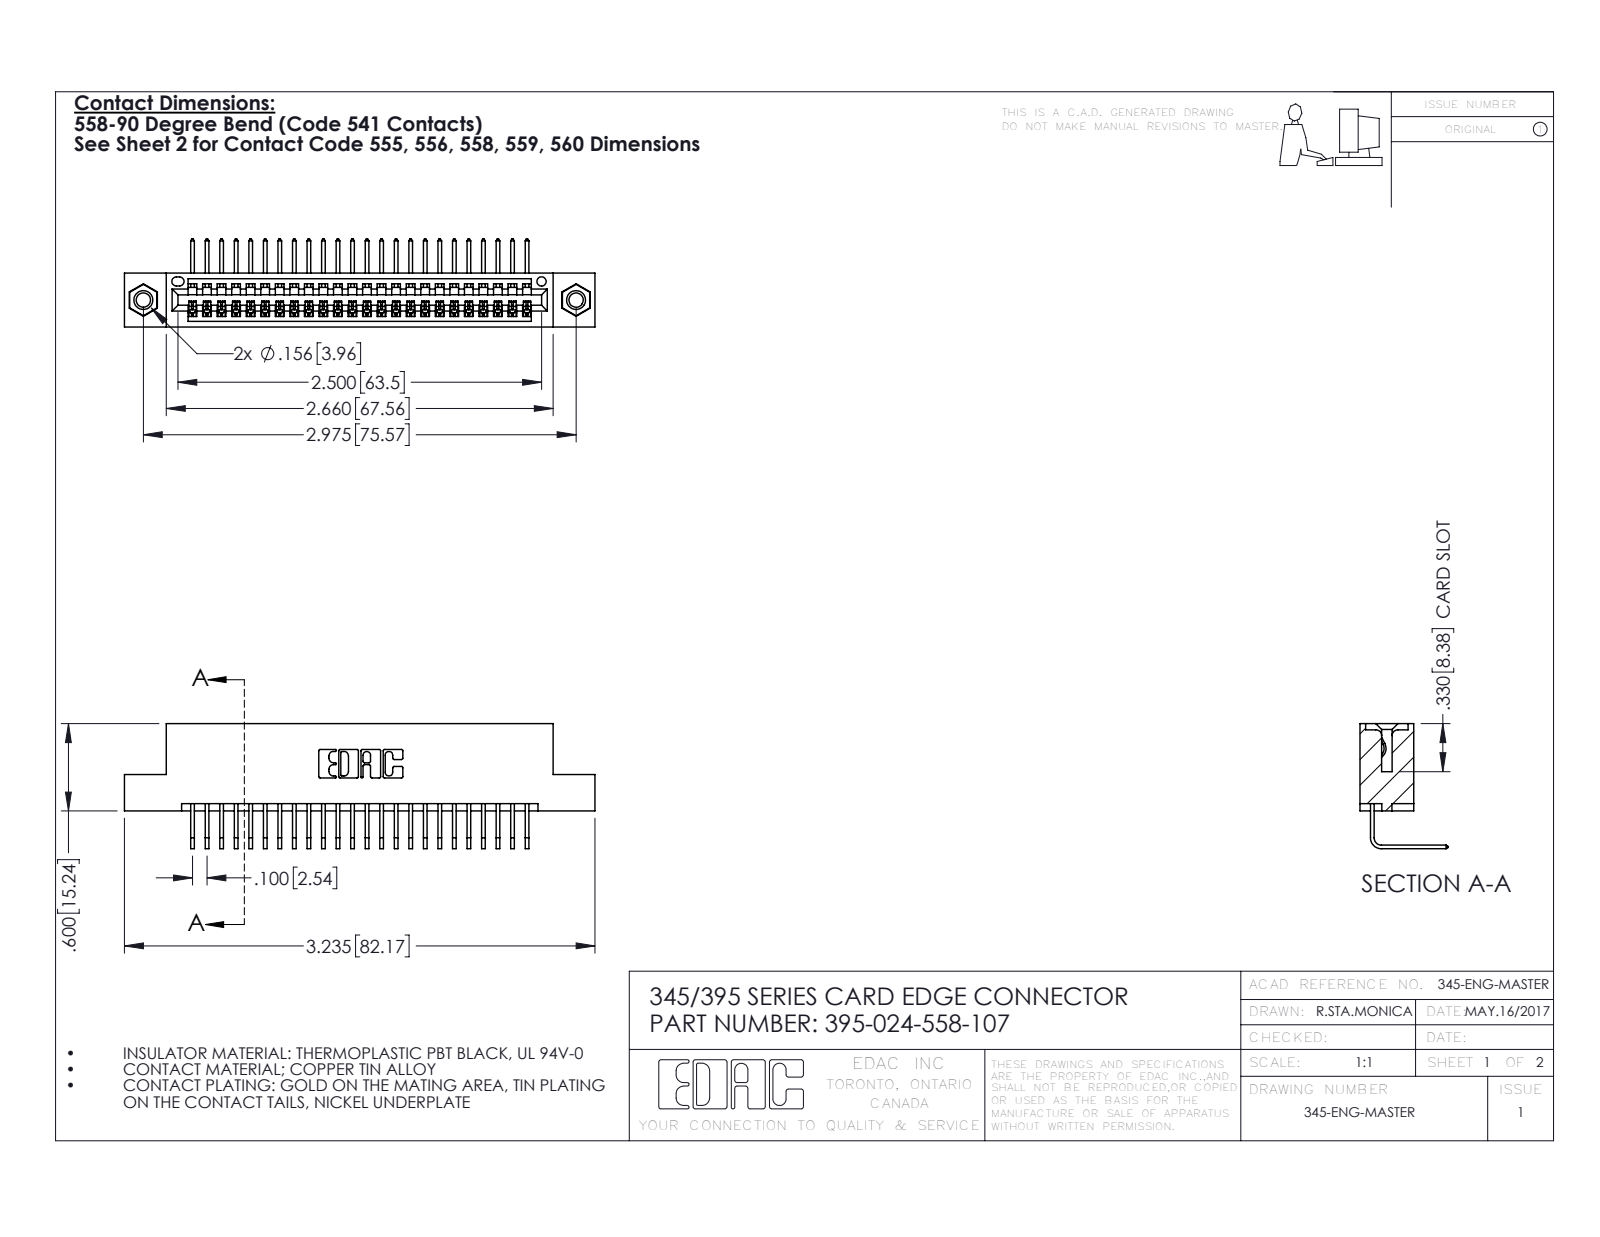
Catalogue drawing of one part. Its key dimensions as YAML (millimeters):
part_name: "345 Part_Flush Mounting Lugs - 0.156 Dia-TI; 395-024-558-107; 345-292-001_558 Tail - 2; 345-250-001_345-250-005-103"
step_written_by: "SolidWorks 2016 (CONFIG_CONTROL_DESIGN)"
units: millimeters
bodies: {solids: 27, faces: 1626, planar: 1120, cylindrical: 490, other: 16}
overall_size: [82.2, 21.8, 15.4]
volume: 7720
surface_area: 10520
round_holes:
  - {diameter: 2.5, count: 2}
  - {diameter: 3.2, count: 2}
  - {diameter: 4, count: 2}
  - {diameter: 1.6, count: 1}
round_bosses_or_shafts:
  - {diameter: 3.9, count: 2}
partial_cylinders:
  - {radius: 0.2, count: 48}
  - {radius: 0.3, count: 22}
  - {radius: 0.2, count: 6}
  - {radius: 0.8, count: 6}
  - {radius: 0.7, count: 3}
  - {radius: 0.8, count: 2}
  - {radius: 1, count: 2}
  - {radius: 0.4, count: 1}
face_to_face_distances: [1.8, 7.6, 5.1, 9.4, 2.5, 6.9, 0.6, 5.7, 3.8, 1.8]
hole_center_spacings: [6.9, 69.6, 75.6]
